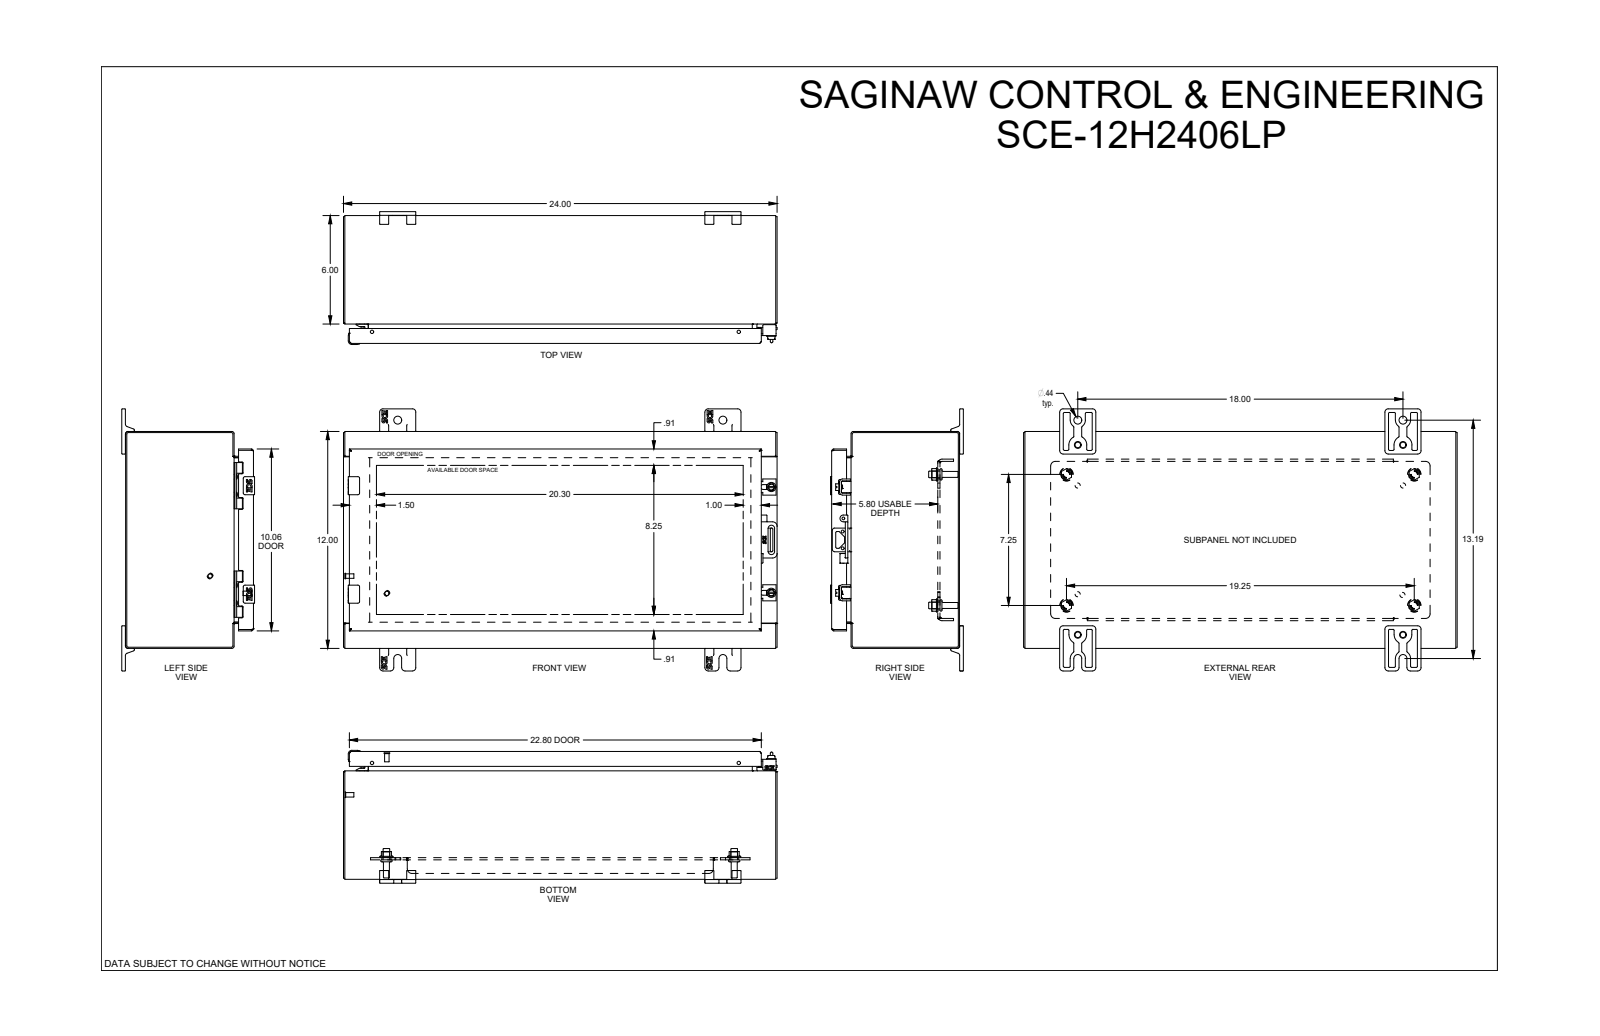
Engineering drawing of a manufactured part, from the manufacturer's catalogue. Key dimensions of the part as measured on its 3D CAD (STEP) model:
Part name (STEP PRODUCT): SCE-12H2406LP
STEP written by: SolidWorks 2019 (AUTOMOTIVE_DESIGN)
Units: inches
Bodies: 56 solids, 3012 faces (1149 planar, 816 cylindrical, 1047 other)
Overall size (bounding box): 24 × 14.5 × 7.348
Volume: 124.8 in³ · Surface area: 2 936 in²
Round holes (diameter × count): ⌀0.172 ×4, ⌀0.205 ×4, ⌀0.218 ×4, ⌀0.244 ×4, ⌀0.266 ×4, ⌀0.281 ×4, ⌀0.31 ×4, ⌀0.312 ×4, ⌀0.367 ×4, ⌀0.375 ×4, ⌀0.437 ×4, ⌀0.5 ×4
Round bosses / shafts (diameter × count): ⌀0.17 ×7, ⌀0.25 ×6, ⌀0.248 ×5, ⌀0.59 ×4, ⌀0.376 ×4, ⌀0.366 ×4, ⌀0.332 ×4, ⌀0.24 ×4
Partial cylindrical surfaces — rounded edges, fillets, slot ends (radius × count): R0.01 ×114, R0.025 ×88, R0.015 ×48, R0.03 ×32, R0.06 ×30, R0.185 ×21, R0.029 ×18, R0.1 ×12
Main face-to-face distances: 0.075, 11.925, 0.06, 7.013, 7.073, 6.998, 6.938, 1.2, 1.125, 5.813
Hole centre spacings: 0.02, 0.493, 0.875, 0.985, 1.741, 6, 8.897, 18.696
